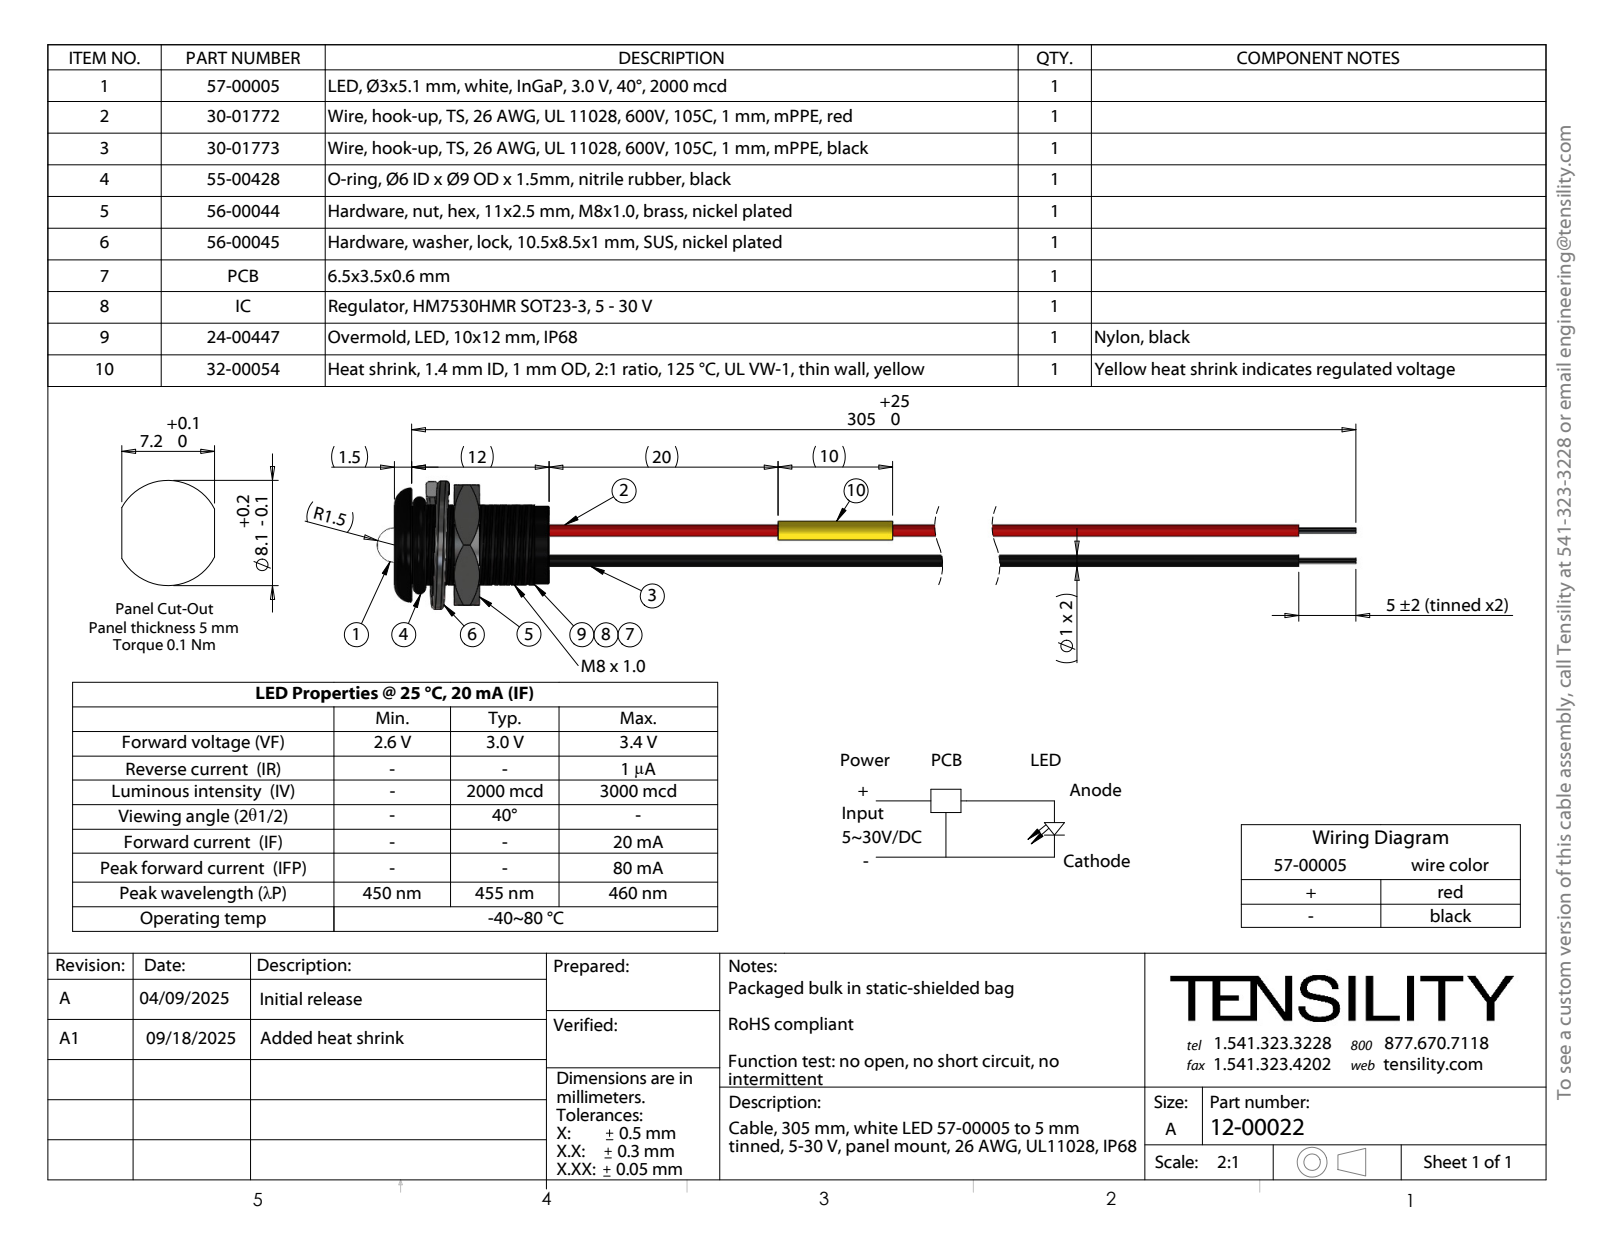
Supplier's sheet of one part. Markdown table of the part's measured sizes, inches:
| quantity | value |
| --- | --- |
| part name | 12-00022; 30-01772_stripped and tinned; 57-00005_trimmed leads; 56-00044 (+4 more) |
| STEP written by | SolidWorks 2021 (CONFIG_CONTROL_DESIGN) |
| units | inches |
| bodies | 57 solids, 555 faces (186 planar, 246 cylindrical, 123 other) |
| overall size | 6.693 × 0.477 × 0.441 |
| volume | 0.061 in³ |
| surface area | 9.157 in² |
| round holes (diameter × count) | 0.039 × 2 |
| round bosses / shafts (diameter × count) | 0.039 × 2, 0.02 × 2, 0.268 × 1, 0.118 × 1 |
| partial cylindrical surfaces (radius × count) | 0.137 × 1, 0.157 × 1 |
| main face-to-face distances | 0.059, 0.531, 0.472, 0.413, 0.205, 0.146, 0.326, 0.292, 0.233, 0.087 |
| hole center spacings | 0.014, 0.015, 0.013, 0.098, 0.099, 0.096, 0.096, 0.101 |
